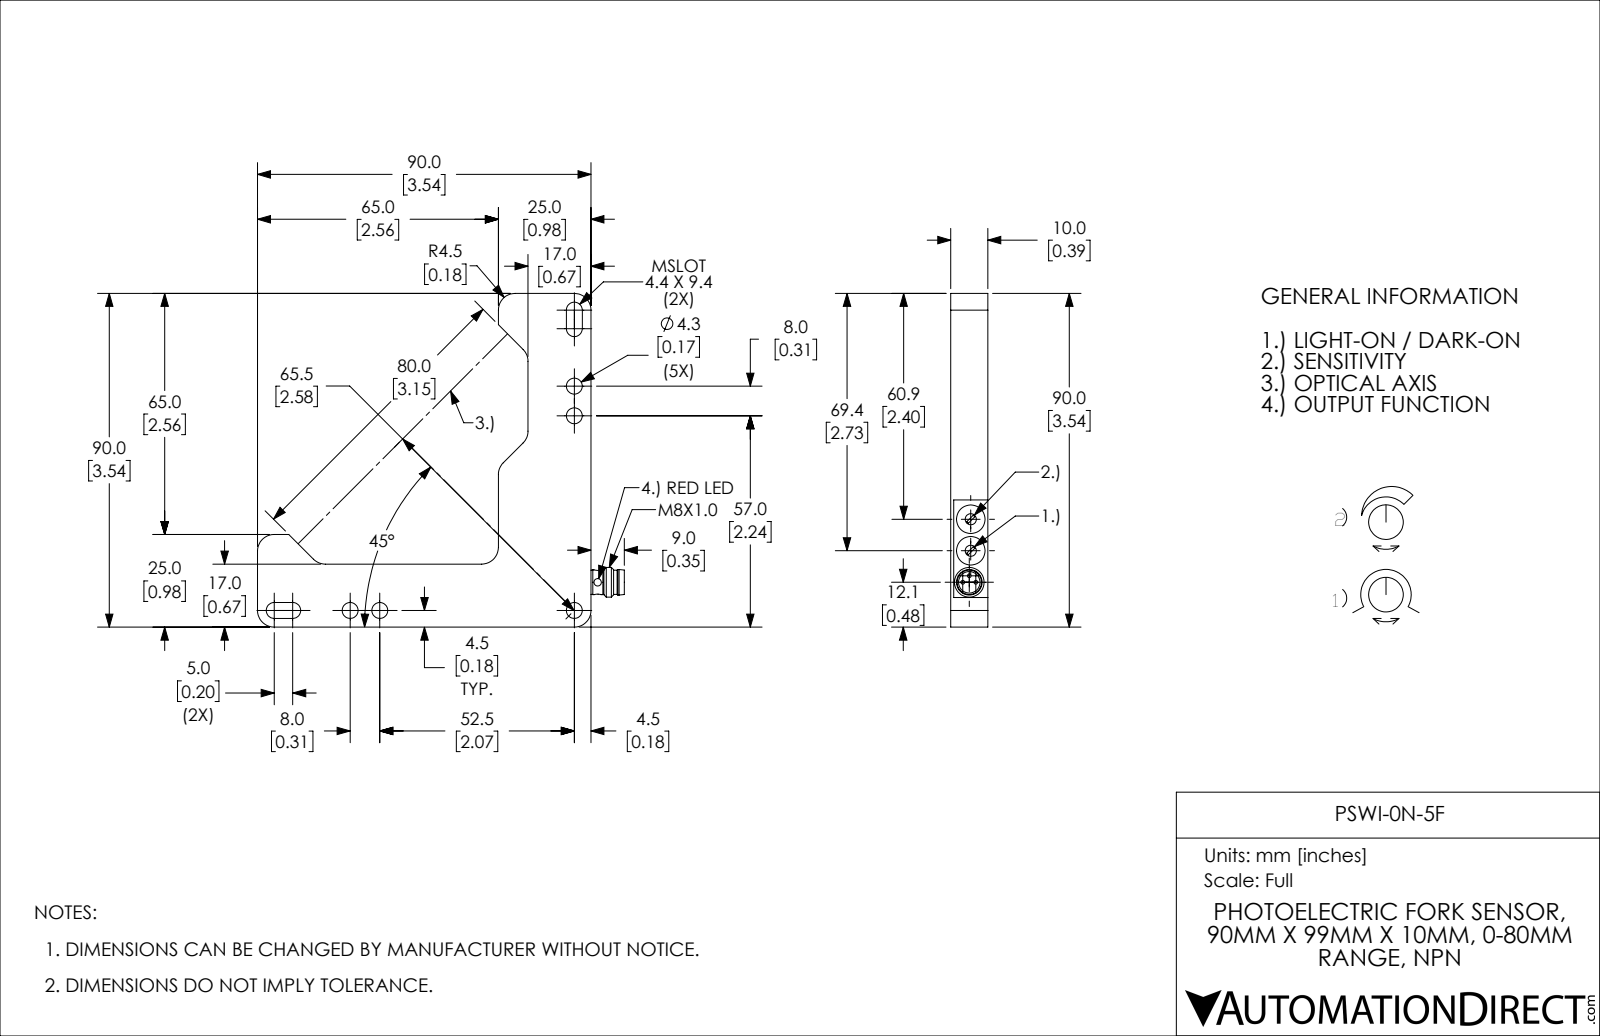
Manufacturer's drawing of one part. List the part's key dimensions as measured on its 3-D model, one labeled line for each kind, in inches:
Part name (STEP PRODUCT): PSWI-0N-5F
STEP written by: SolidWorks 2017 (AUTOMOTIVE_DESIGN)
Units: inches
Bodies: 1 solid, 90 faces (42 planar, 41 cylindrical, 7 other)
Overall size (bounding box): 3.898 × 3.543 × 0.394
Volume: 1.872 in³ · Surface area: 17.48 in²
Round holes (diameter × count): ⌀0.169 ×5, ⌀0.079 ×2, ⌀0.118 ×2, ⌀0.303 ×2, ⌀0.228 ×1
Round bosses / shafts (diameter × count): ⌀0.039 ×3, ⌀0.315 ×1, ⌀0.272 ×1, ⌀0.264 ×1, ⌀0.257 ×1
Partial cylindrical surfaces — rounded edges, fillets, slot ends (radius × count): R0.177 ×10, R0.085 ×4, R0.049 ×2
Main face-to-face distances: 0.394, 0.669, 3.543, 2.874, 0.984, 0.315, 2.559, 3.539, 0.98, 0.665
Hole centre spacings: 0.315, 2.067, 2.382, 3.154, 0.335, 0.335, 0.389, 0.669
